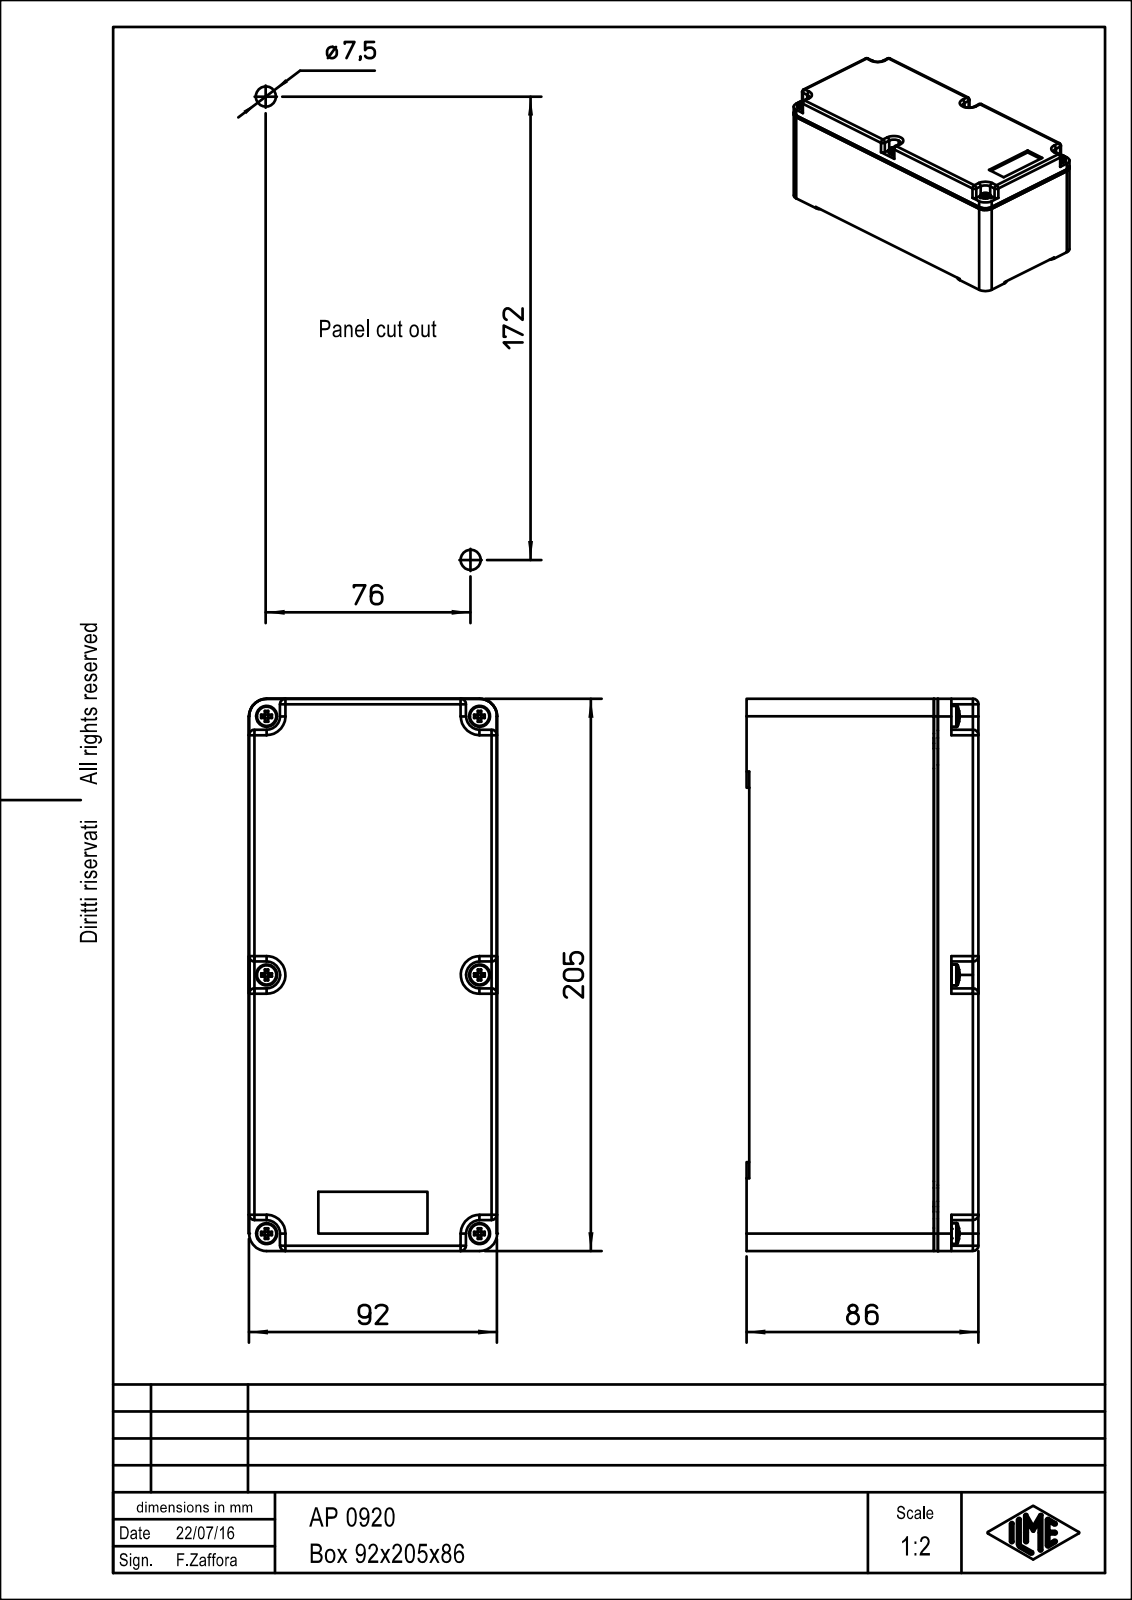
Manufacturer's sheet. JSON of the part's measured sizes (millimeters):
{"part_name": "COVER; BOX; AP_0920", "step_written_by": "PTC Creo Elements/Direct Modeling 19.0B 21-Mar-2015 (C) Parametric Technology GmbH (AUTOMOTIVE_DESIGN)", "units": "millimeters", "bodies": {"solids": 2, "faces": 1109, "planar": 844, "cylindrical": 211, "other": 54}, "overall_size": [205.02, 92.02, 86], "volume_mm3": 375175, "surface_area_mm2": 188934, "round_holes": [[3.3, 8], [4.5, 6], [5.8, 2], [7.5, 2], [10.6, 1], [10.61, 1]], "round_bosses_or_shafts": [[7.8, 6], [4, 6], [6.2, 2], [6, 2], [7, 1]], "partial_cylinders_radius": [[2, 23], [0.33, 22], [6, 12], [5, 8], [6.5, 8], [8, 8], [0.27, 4], [0.27, 4]], "face_to_face_distances": [3, 82, 85, 92, 79, 4.38, 4.37, 87.63, 83.25, 13.5], "hole_center_spacings": [79, 124.33, 96, 78.14, 95.99, 96.01, 124.32, 192]}
